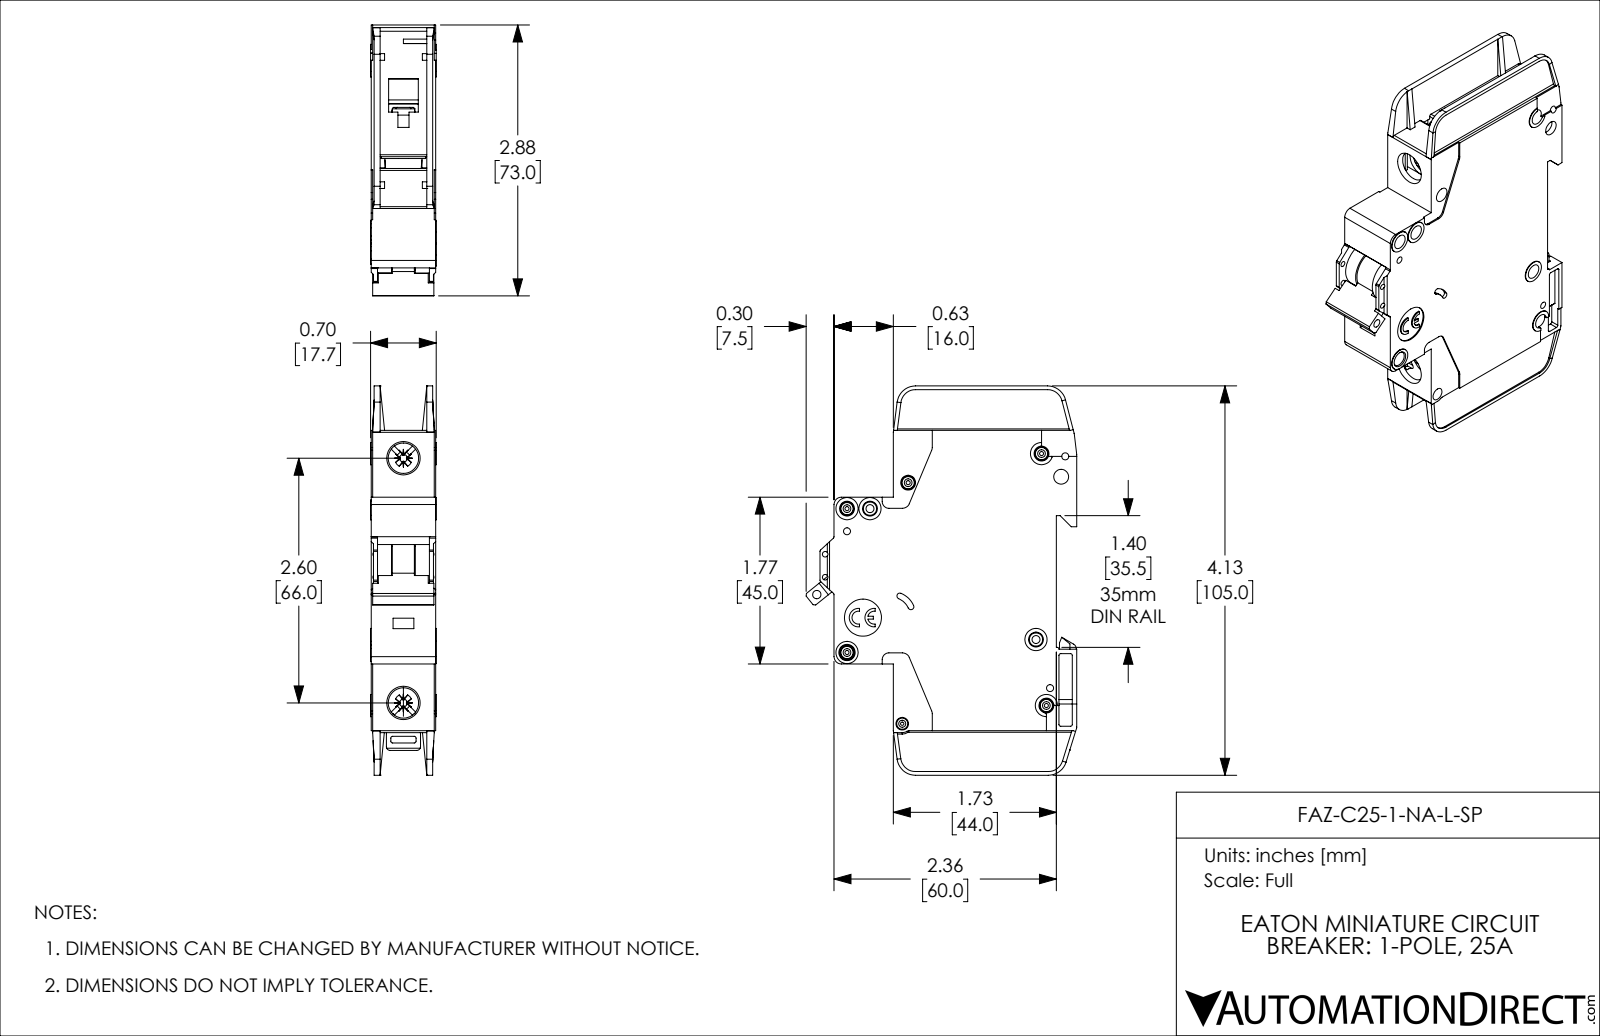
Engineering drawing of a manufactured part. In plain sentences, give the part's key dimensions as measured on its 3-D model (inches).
The part is named "FAZ-C25-1-NA-L-SP". Its 3-D file was written by "SolidWorks 2019 (AUTOMOTIVE_DESIGN)". It is 1 solid with 1127 faces: 671 planar, 357 cylindrical and 99 other. Overall it measures 4.134 by 2.876 by 0.697 inches. Its volume is 4.682 cubic inches and its surface area 41.01 square inches. Round holes: 8 of diameter 0.157, 5 of diameter 0.043, 4 of diameter 0.075, 2 of diameter 0.059, 2 of diameter 0.085, 2 of diameter 0.323, 1 of diameter 0.035, 1 of diameter 0.089, 1 of diameter 0.098, 1 of diameter 0.134, 1 of diameter 0.394. Round bosses or shafts: 5 of diameter 0.13, 4 of diameter 0.236, 2 of diameter 0.118, 1 of diameter 0.098. Partial cylindrical surfaces (rounded edges, fillets, slot ends): 42 of radius 0.02, 10 of radius 0.016, 10 of radius 0.039, 8 of radius 0.079, 5 of radius 0.197, 4 of radius 0.008, 4 of radius 0.026, 4 of radius 0.043. The main face-to-face distances are 0.047, 0.685, 0.591, 0.638, 0.094, 0.543, 0.016, 0.031, 0.496, 0.575. The hole center spacings are 0.244, 0.537, 0.87, 0.189, 0.199, 0.204, 0.221, 0.24.
